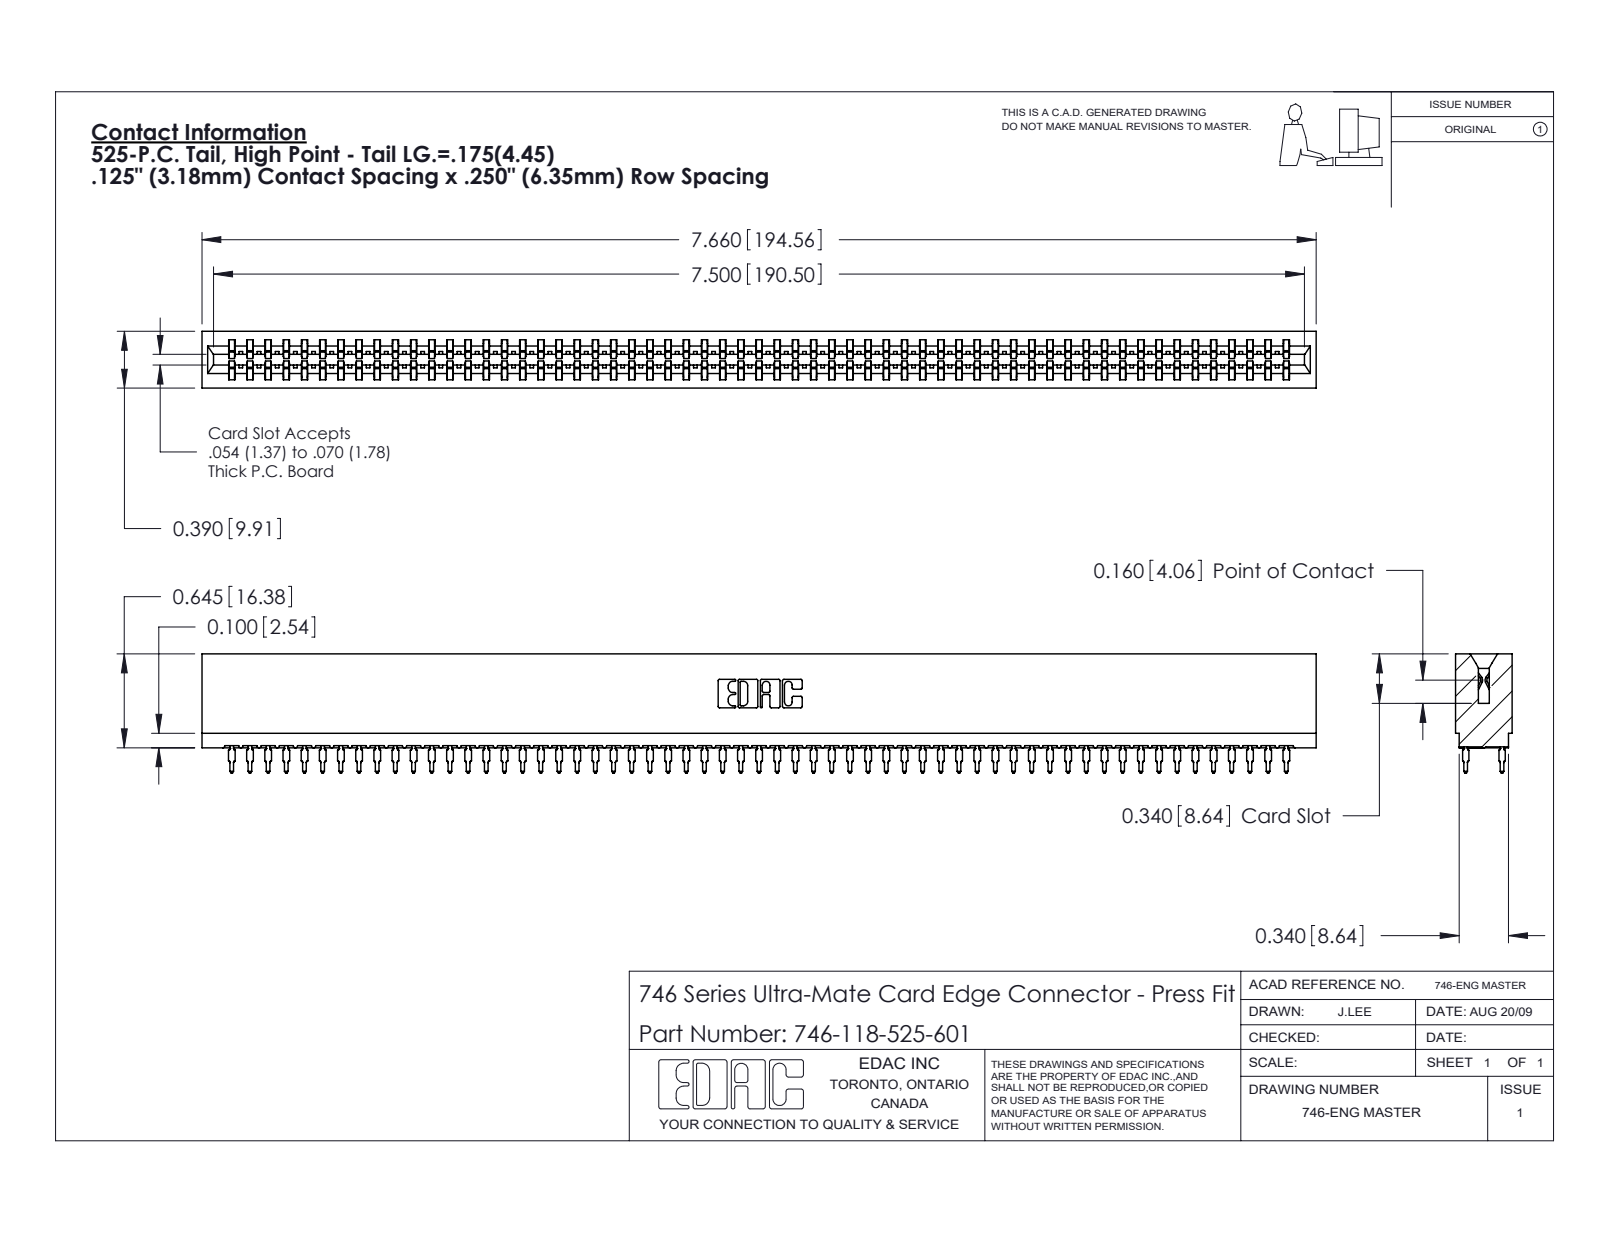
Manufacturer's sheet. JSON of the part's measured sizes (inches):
{"part_name": "746-292-001_525; 746 Part_.340 Slot Depth - 01; 746-118-525-601", "step_written_by": "SolidWorks 2020 (CONFIG_CONTROL_DESIGN)", "units": "inches", "bodies": {"solids": 119, "faces": 10658, "planar": 5483, "cylindrical": 2107, "other": 3068}, "overall_size": [7.66, 0.819, 0.39], "volume_in3": 1.356, "surface_area_in2": 50.48, "partial_cylinders_radius": [[0.021, 236], [0.015, 60], [0.01, 22], [0.005, 8], [0.011, 8], [0.007, 6], [0.031, 6], [0.026, 3]], "face_to_face_distances": [0.057, 0.333, 0.39, 0.025, 0.25, 0.307, 0.275, 0.083, 0.015, 0.059]}
